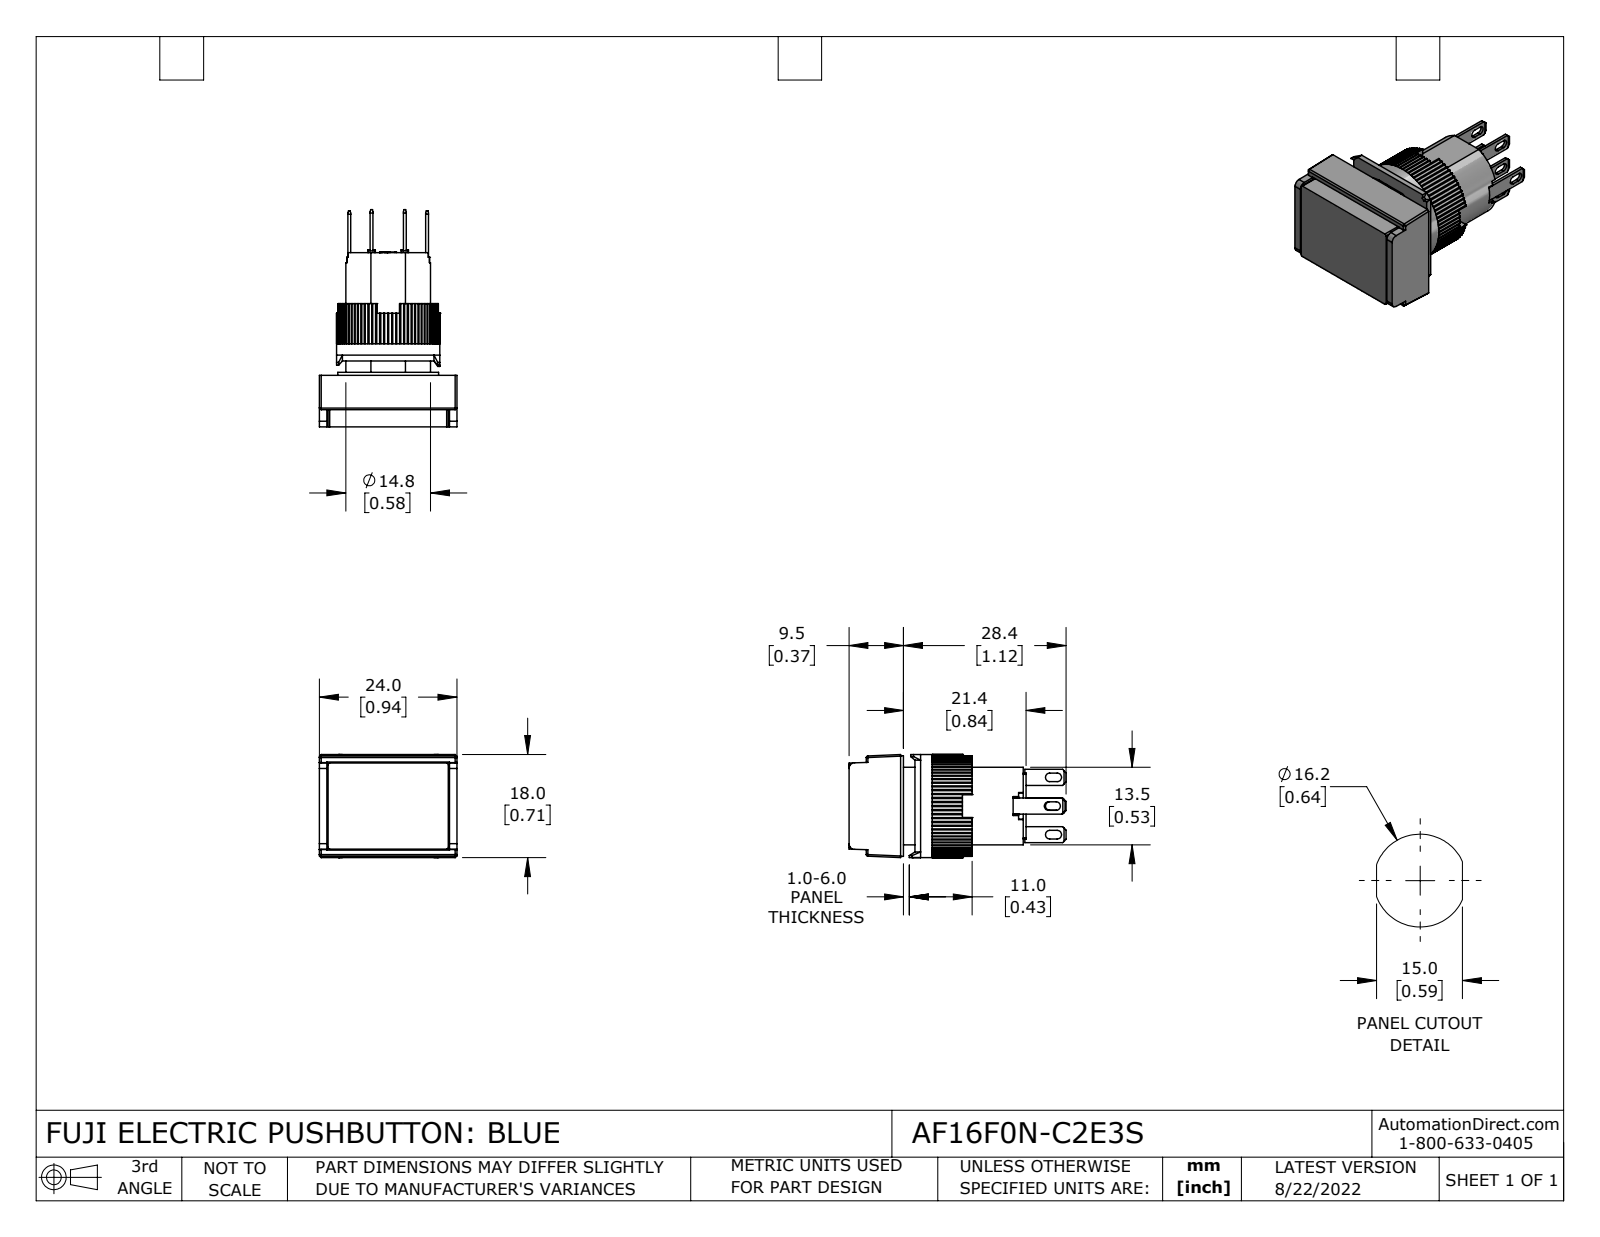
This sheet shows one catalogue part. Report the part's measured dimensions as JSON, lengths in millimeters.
{"part_name": "AF16F0N-C2E3S", "step_written_by": "SolidWorks 2023 (CONFIG_CONTROL_DESIGN)", "units": "millimeters", "bodies": {"solids": 14, "faces": 845, "planar": 656, "cylindrical": 185, "other": 4}, "overall_size": [37.9, 24, 18], "volume_mm3": 7690, "surface_area_mm2": 6103, "round_holes": [[13.8, 1], [14.8, 1]], "round_bosses_or_shafts": [[18, 1], [17.6, 1]], "partial_cylinders_radius": [[0.3, 80], [0.2, 12], [0.8, 8], [0.3, 6], [1, 2], [8, 1]], "face_to_face_distances": [5.4, 9, 3.6, 8.9, 12.5, 17.9, 3.5, 0.5, 21.4, 19.4]}
